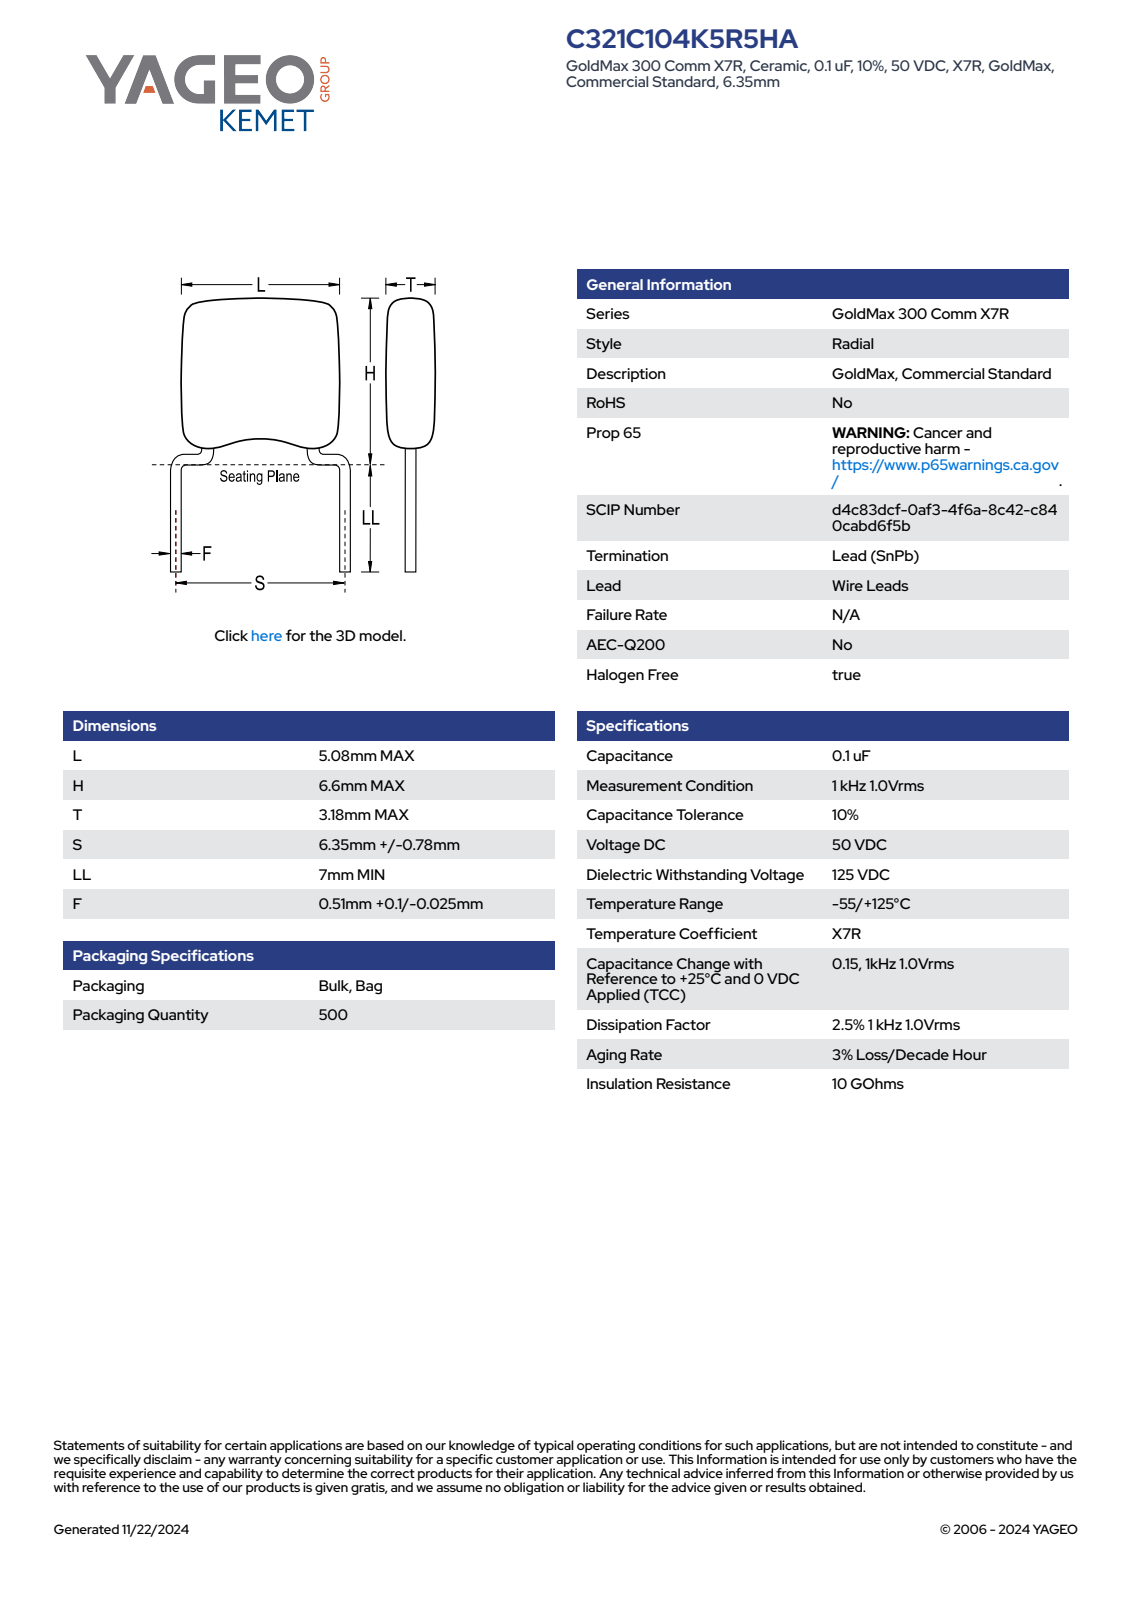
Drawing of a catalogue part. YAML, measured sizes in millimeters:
part_name: "CCR_SB_5.08X6.6_L5.08H6.6T3.18S6.35LL7F0.51"
step_written_by: "SolidWorks 2014 (AUTOMOTIVE_DESIGN)"
units: millimeters
bodies: {solids: 4, faces: 97, planar: 65, cylindrical: 14, other: 18}
overall_size: [13.6, 6.86, 3.19]
volume: 73
surface_area: 123
round_bosses_or_shafts:
  - {diameter: 0.51, count: 2}
partial_cylinders:
  - {radius: 1, count: 10}
face_to_face_distances: [3.18, 5.08, 4.81, 3.19, 0.43, 2.64, 2.17, 2.21, 2.6, 0.39]
